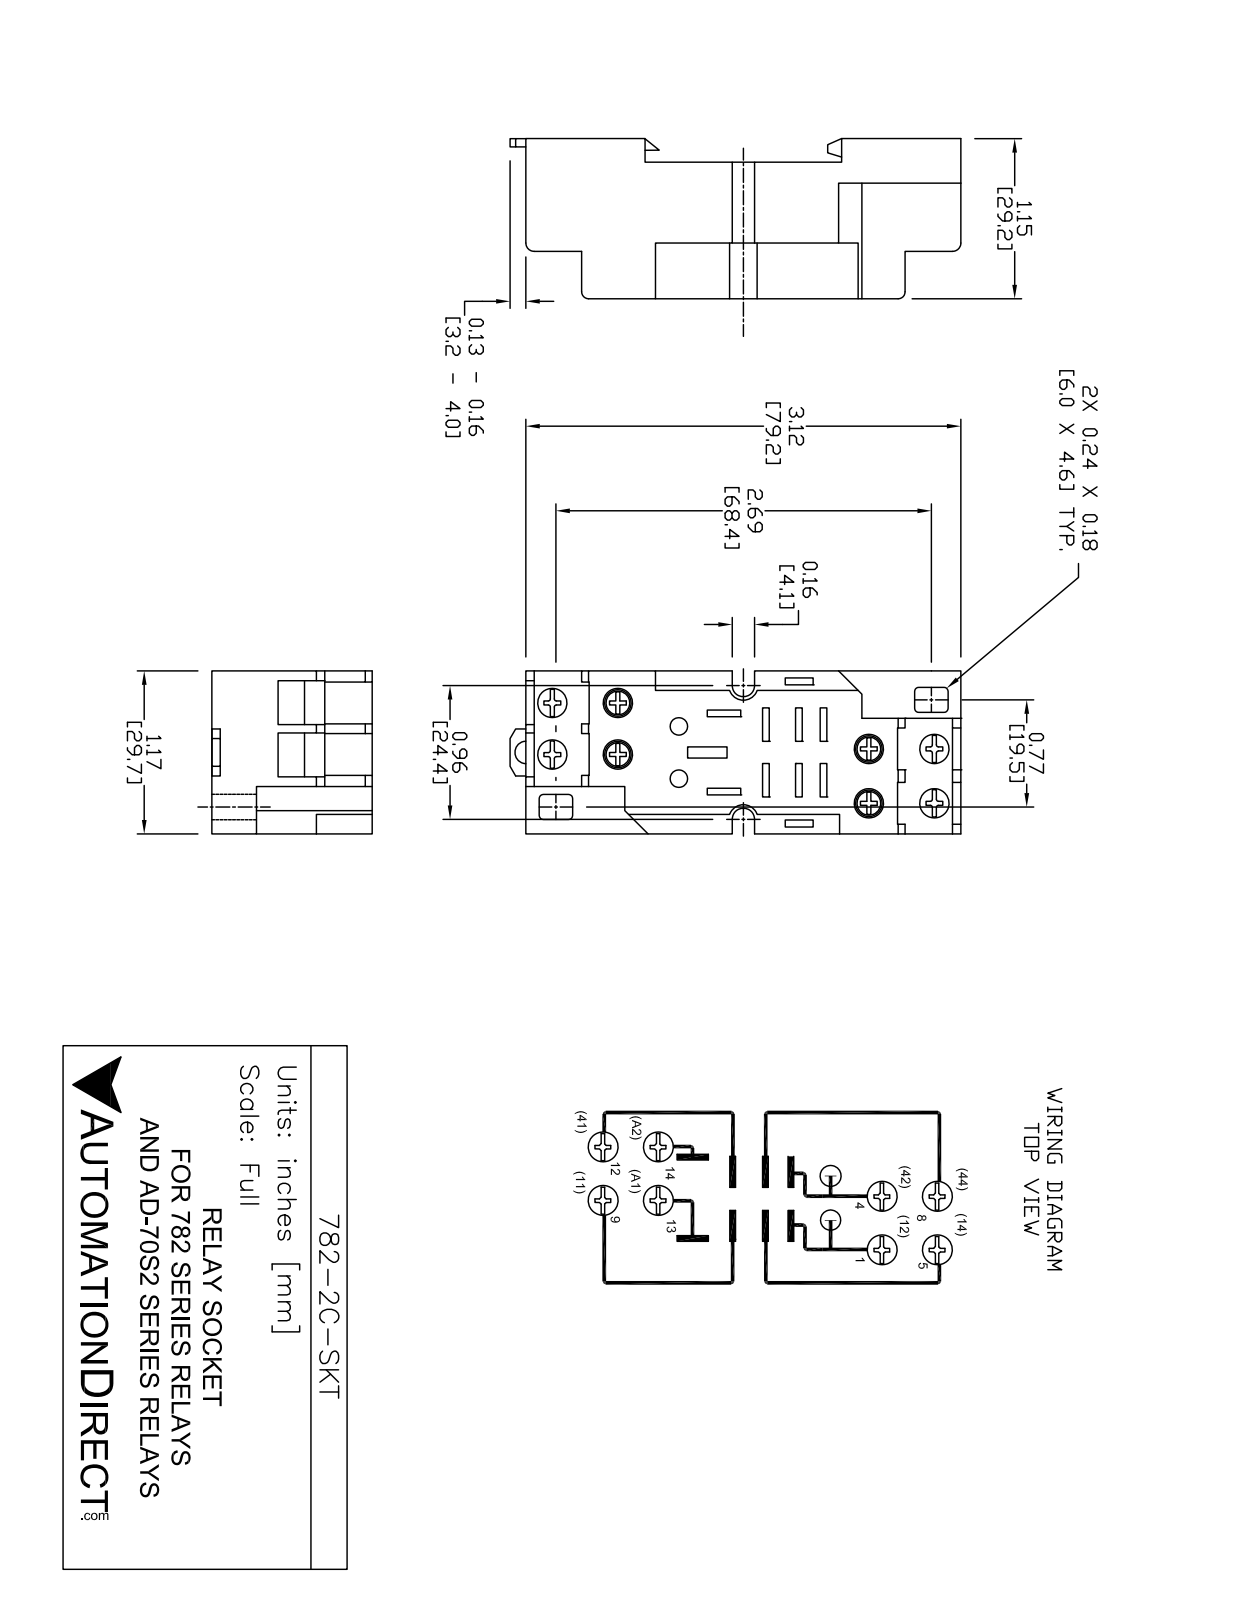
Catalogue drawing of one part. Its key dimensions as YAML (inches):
part_name: "782-2C-SKT"
step_written_by: "SolidWorks 2017 (AUTOMOTIVE_DESIGN)"
units: inches
bodies: {solids: 5, faces: 358, planar: 280, cylindrical: 70, other: 8}
overall_size: [3.233, 1.17, 1.15]
volume: 2.888
surface_area: 21.91
round_holes:
  - {diameter: 0.21, count: 8}
  - {diameter: 0.125, count: 2}
round_bosses_or_shafts:
  - {diameter: 0.19, count: 4}
partial_cylinders:
  - {radius: 0.015, count: 16}
  - {radius: 0.03, count: 8}
  - {radius: 0.05, count: 2}
  - {radius: 0.06, count: 2}
  - {radius: 0.08, count: 2}
  - {radius: 0.105, count: 2}
  - {radius: 0.081, count: 1}
face_to_face_distances: [0.98, 1.17, 0.17, 1.15, 0.34, 0.83, 0.14, 1.03, 0.2, 0.69]
hole_center_spacings: [0.47, 0.37, 0.39, 0.598, 0.611, 2.27, 2.294, 2.297]
